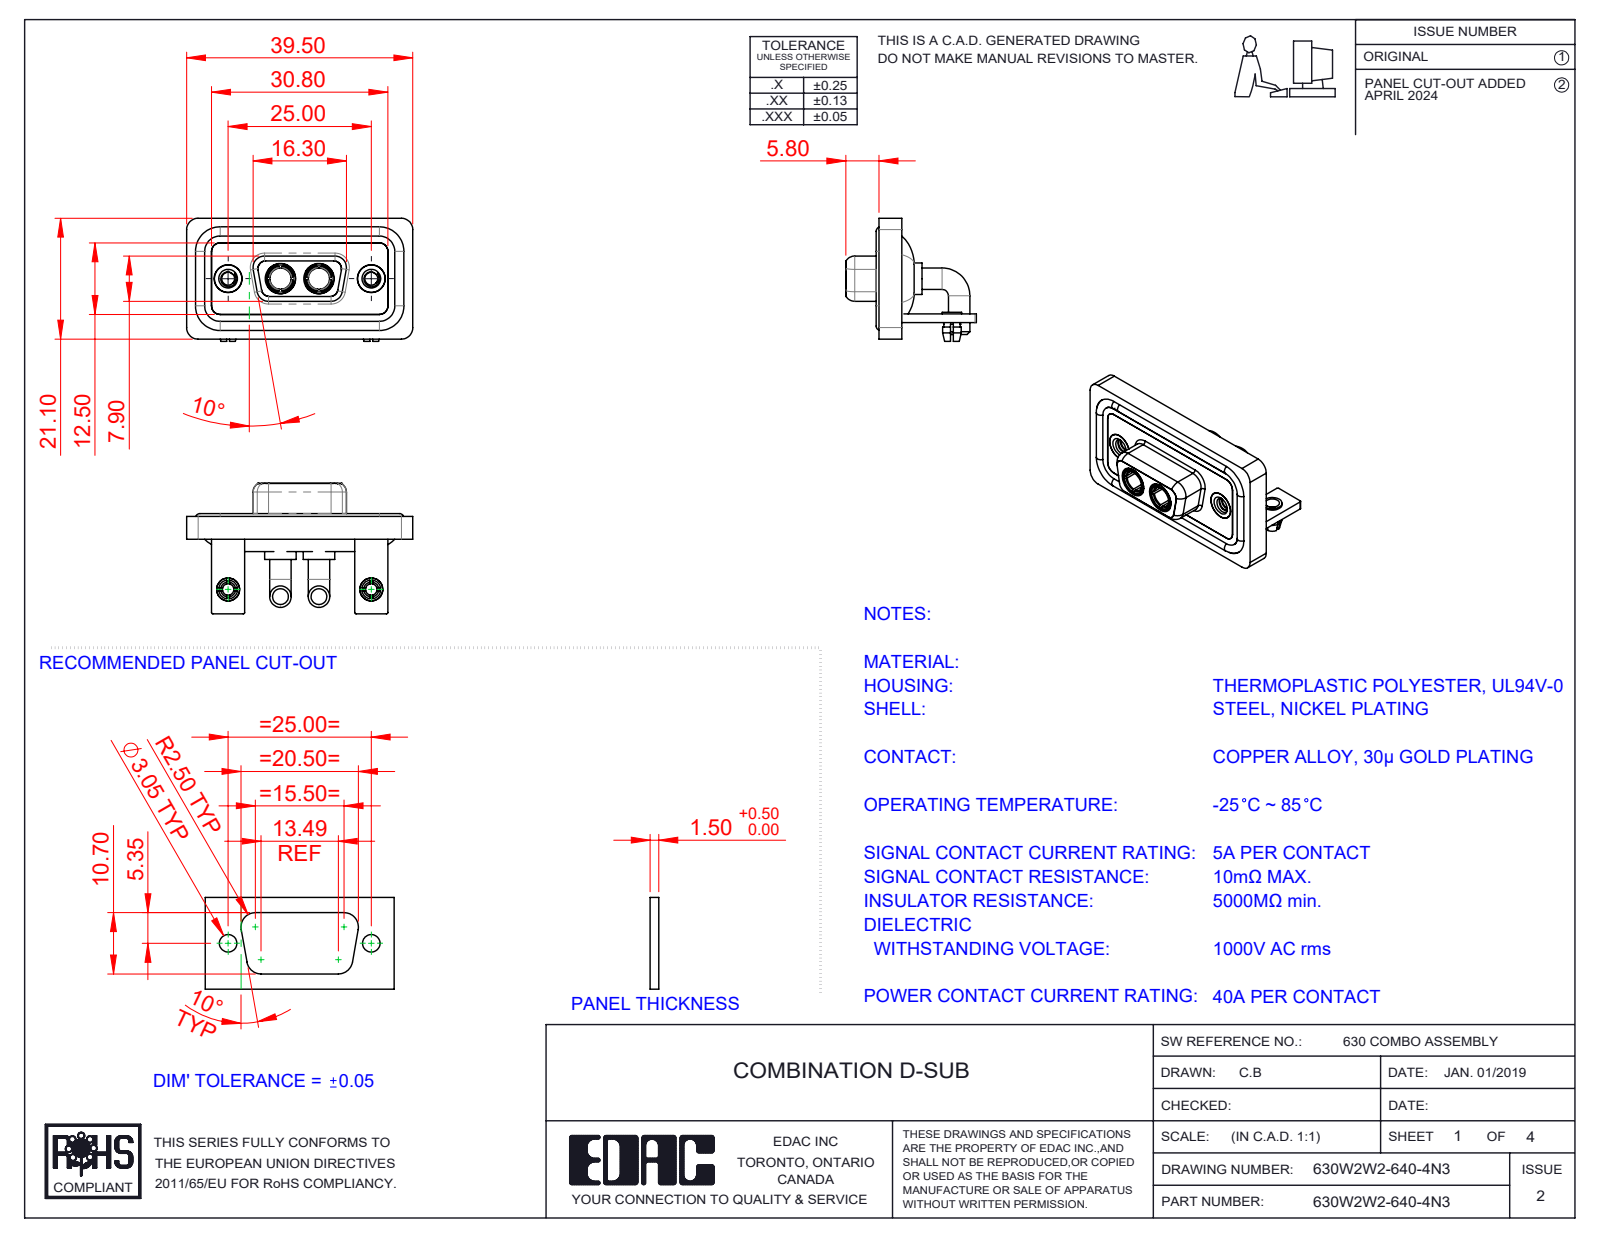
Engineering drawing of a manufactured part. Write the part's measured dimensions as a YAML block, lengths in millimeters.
part_name: "630Combo Shell Rear_09 Contacts; 630Combo Stabilizer Bracket_50 Contacts; 630Combo Waterproof Housing_09 Contacts; 630W2W2-640-4N3 (+5 more)"
step_written_by: "SolidWorks 2023 (CONFIG_CONTROL_DESIGN)"
units: millimeters
bodies: {solids: 15, faces: 682, planar: 231, cylindrical: 294, other: 157}
overall_size: [39.5, 22.8, 21.5]
volume: 5364
surface_area: 8819
round_holes:
  - {diameter: 4.85, count: 4}
  - {diameter: 2, count: 2}
  - {diameter: 2.26, count: 2}
  - {diameter: 2.5, count: 2}
  - {diameter: 3.2, count: 2}
  - {diameter: 3.7, count: 2}
  - {diameter: 4, count: 2}
  - {diameter: 4.05, count: 2}
  - {diameter: 5, count: 2}
  - {diameter: 5.3, count: 2}
round_bosses_or_shafts:
  - {diameter: 3.75, count: 4}
  - {diameter: 1.6, count: 4}
  - {diameter: 5.5, count: 2}
  - {diameter: 5.2, count: 2}
  - {diameter: 4.96, count: 2}
  - {diameter: 4.95, count: 2}
  - {diameter: 4.8, count: 2}
  - {diameter: 4.75, count: 2}
partial_cylinders:
  - {radius: 2, count: 19}
  - {radius: 1.5, count: 18}
  - {radius: 0.25, count: 16}
  - {radius: 1.35, count: 8}
  - {radius: 1.6, count: 8}
  - {radius: 0.5, count: 5}
  - {radius: 0.6, count: 4}
  - {radius: 0.65, count: 4}
face_to_face_distances: [0.4, 2.9, 1.5, 1.8, 1.1, 3.7, 0.8, 2.5, 1.6, 3.1]
hole_center_spacings: [9.14, 15.86, 25, 6.72]
